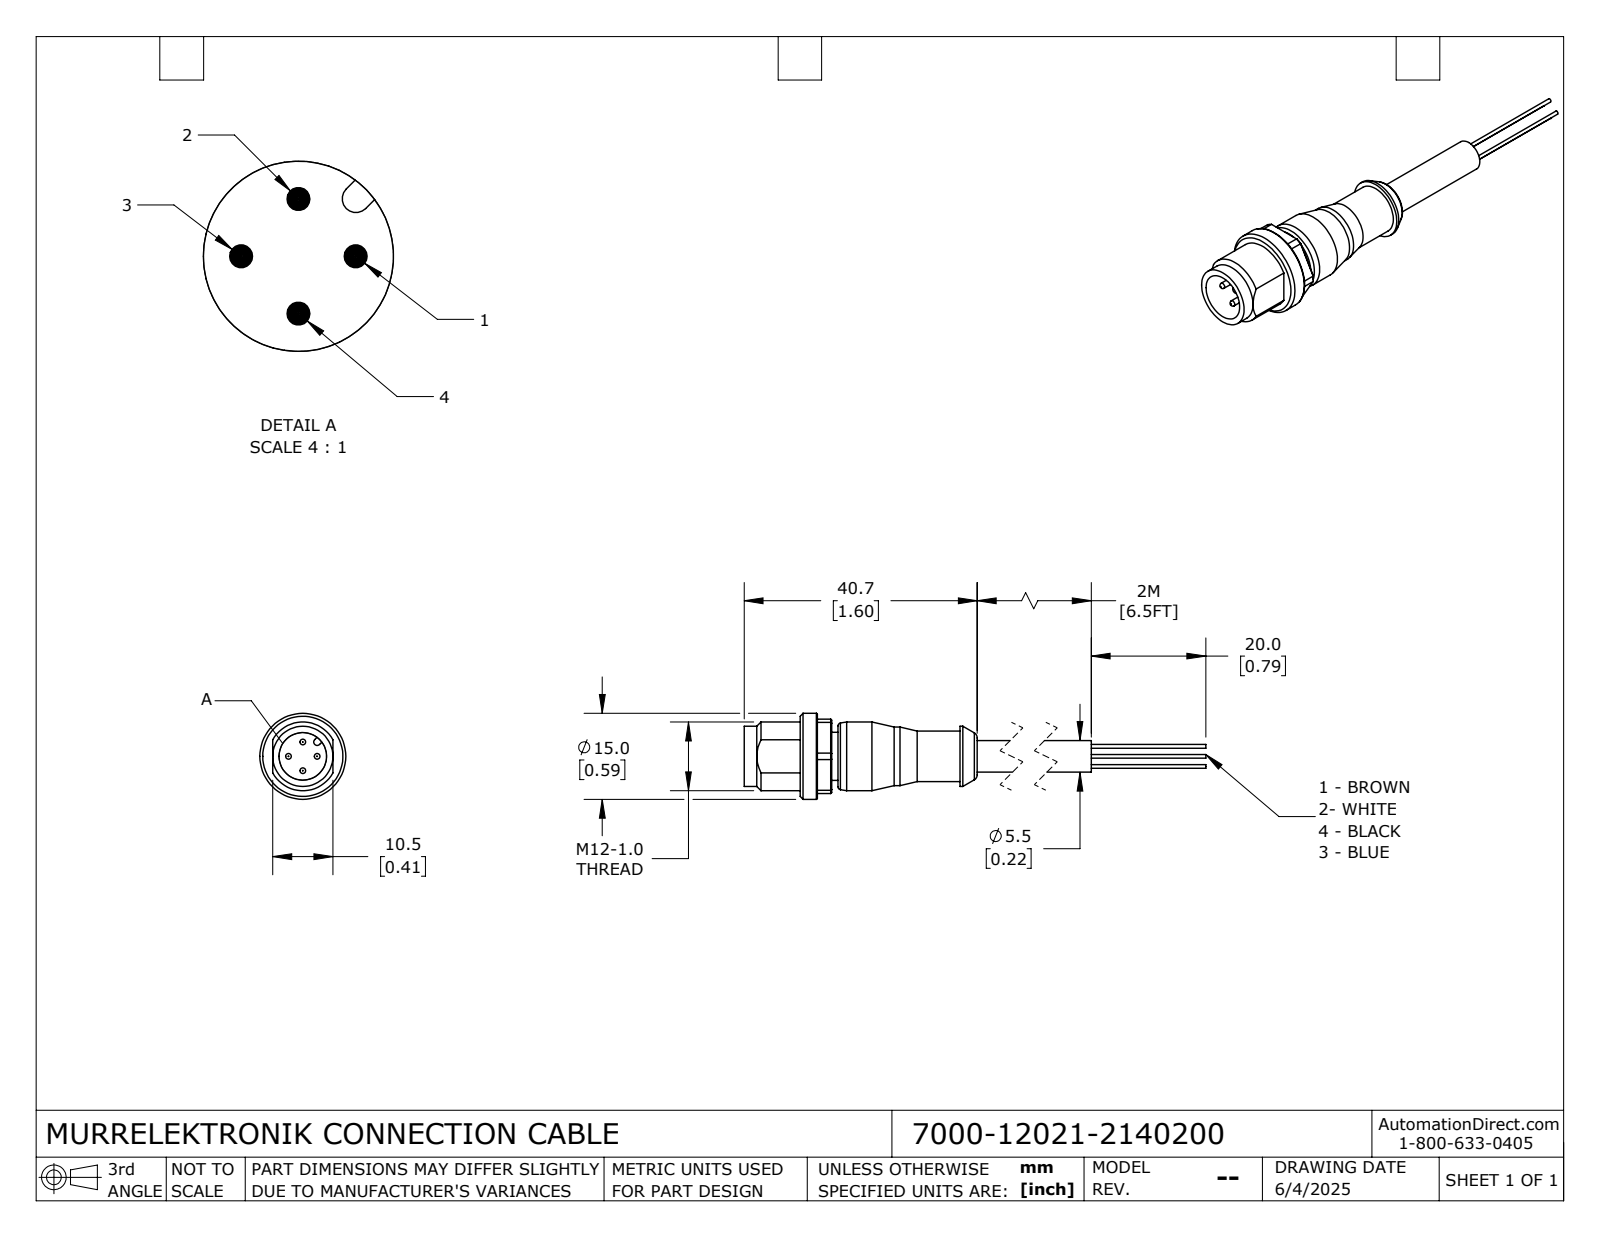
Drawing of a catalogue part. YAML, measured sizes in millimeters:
part_name: "7000-12021-2140200"
step_written_by: "SolidWorks 2024 (CONFIG_CONTROL_DESIGN)"
units: millimeters
bodies: {solids: 1, faces: 110, planar: 34, cylindrical: 43, other: 33}
overall_size: [80.7, 15, 15]
volume: 3989
surface_area: 2637
round_holes:
  - {diameter: 8.3, count: 1}
round_bosses_or_shafts:
  - {diameter: 1, count: 4}
  - {diameter: 0.64, count: 4}
  - {diameter: 15, count: 1}
  - {diameter: 12, count: 1}
  - {diameter: 10.5, count: 1}
  - {diameter: 10.2, count: 1}
  - {diameter: 8.8, count: 1}
  - {diameter: 8.4, count: 1}
partial_cylinders:
  - {radius: 0.6, count: 1}
  - {radius: 7.2, count: 1}
face_to_face_distances: [6.4, 0.9, 5.5, 13, 10.5, 27.9, 7.5, 6.6, 1.1, 8.9]
